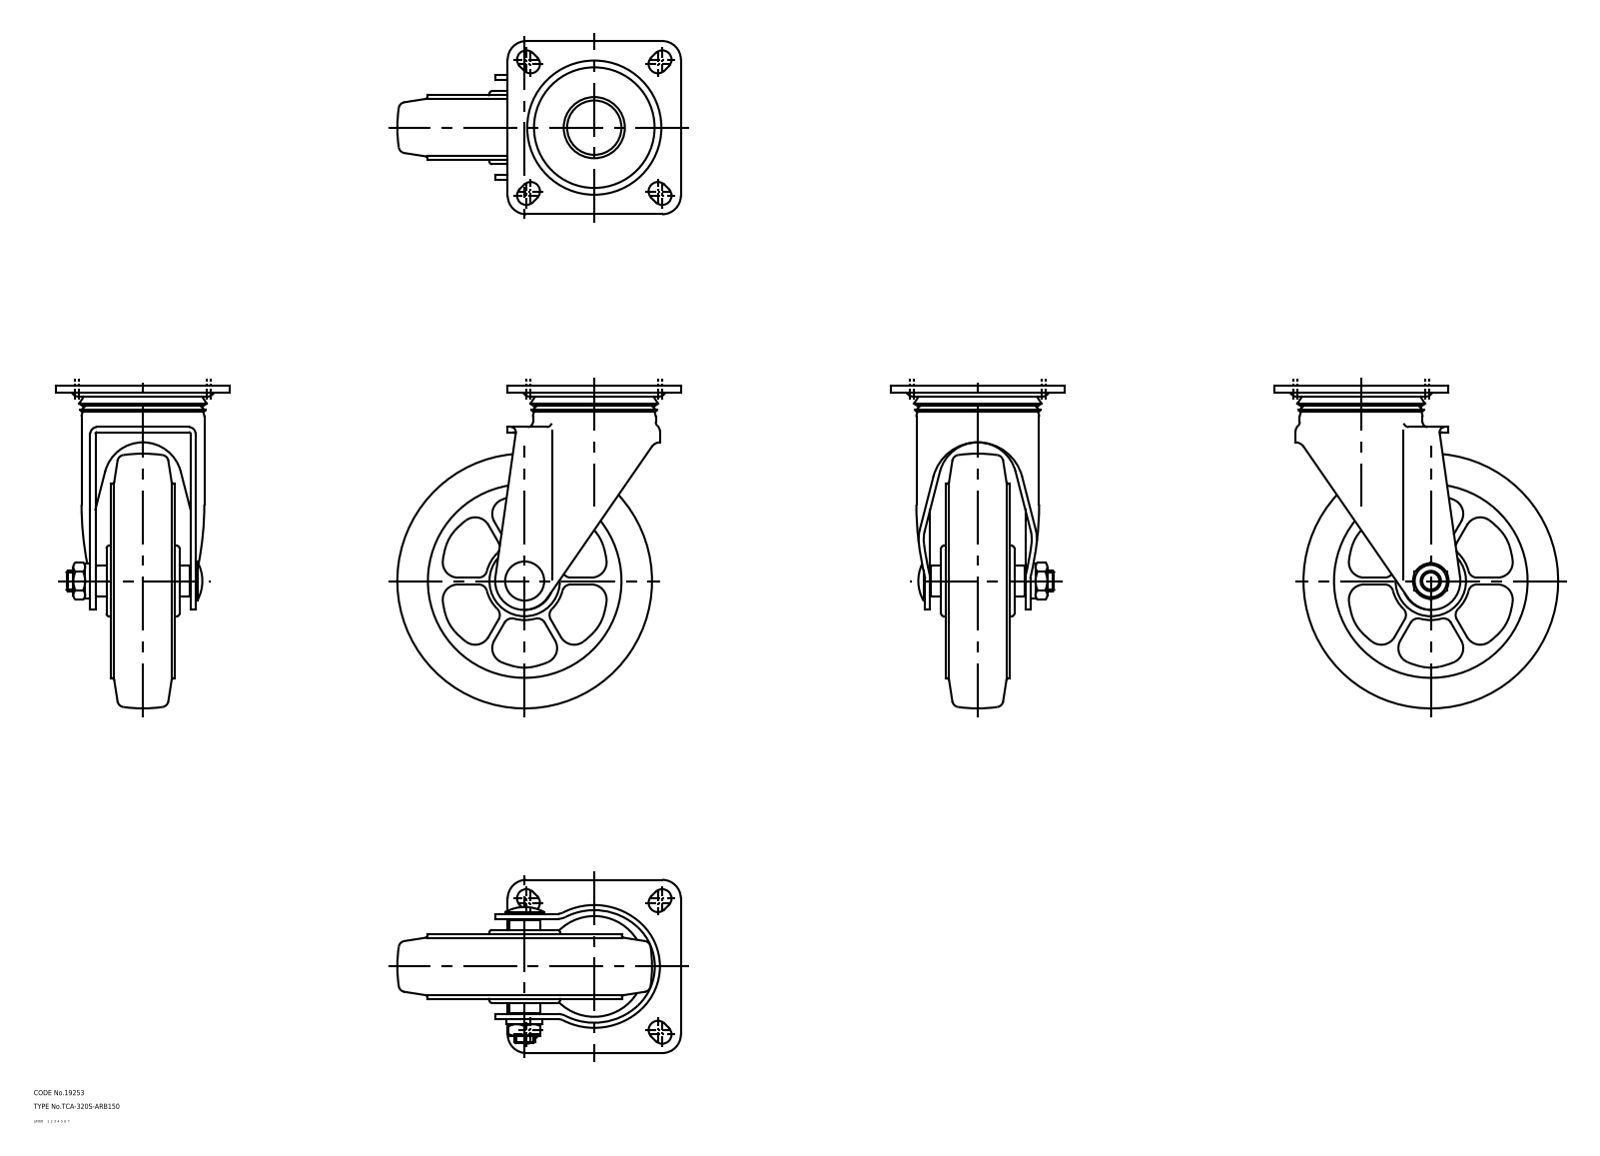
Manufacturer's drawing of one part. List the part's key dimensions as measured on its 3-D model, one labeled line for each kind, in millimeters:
Part name (STEP PRODUCT): wheel; mounting plate; main shaft; axle (+1 more)
STEP written by: CADfix (AUTOMOTIVE_DESIGN)
Units: millimetres
Bodies: 5 solids, 302 faces (0 planar, 0 cylindrical, 302 other)
Overall size (bounding box): 190 × 167 × 102
Volume: 588 444 mm³ · Surface area: 139 912 mm²
